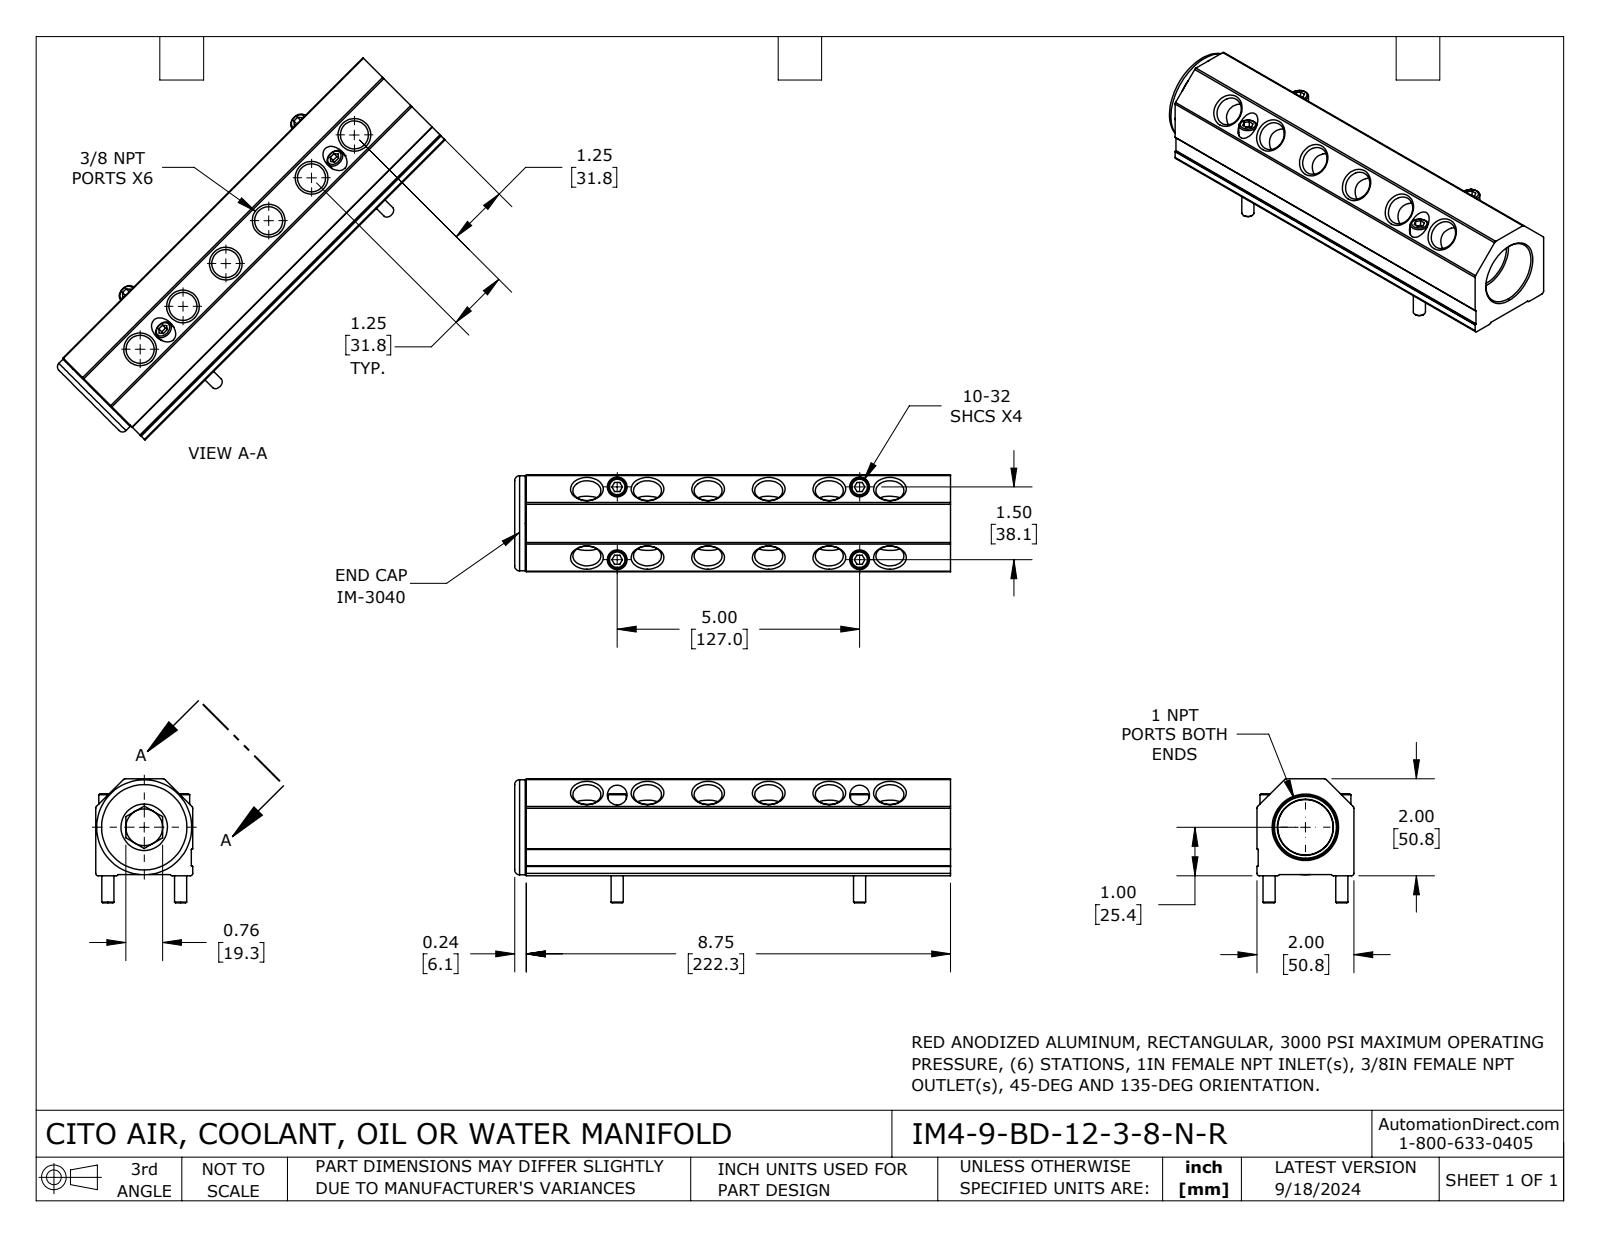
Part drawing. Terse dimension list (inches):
name: IM4-9-BD-12-3-8-N-R
written by: SolidWorks 2023 (CONFIG_CONTROL_DESIGN)
unit: in
bodies: 6 solids, 229 faces (81 planar, 82 cylindrical, 66 other)
size: 8.99 × 2.56 × 2
volume: 21.74 in³; area: 130 in²
holes: 12× ⌀0.578, 4× ⌀0.266, 4× ⌀0.406, 1× ⌀0.758, 1× ⌀1.156, 1× ⌀1.637
bosses: 4× ⌀0.375, 4× ⌀0.25, 1× ⌀1.96, 1× ⌀1.359, 1× ⌀1.293, 1× ⌀1.14
rounds: 8× R0.05, 4× R0.01
face distances: 2, 1.975, 0.025, 0.028, 1.972, 8.75, 0.24, 8.99, 0.764, 0.524
hole spacings: 1.25, 2.5, 3.75, 5, 1.5, 5.22, 6.25
